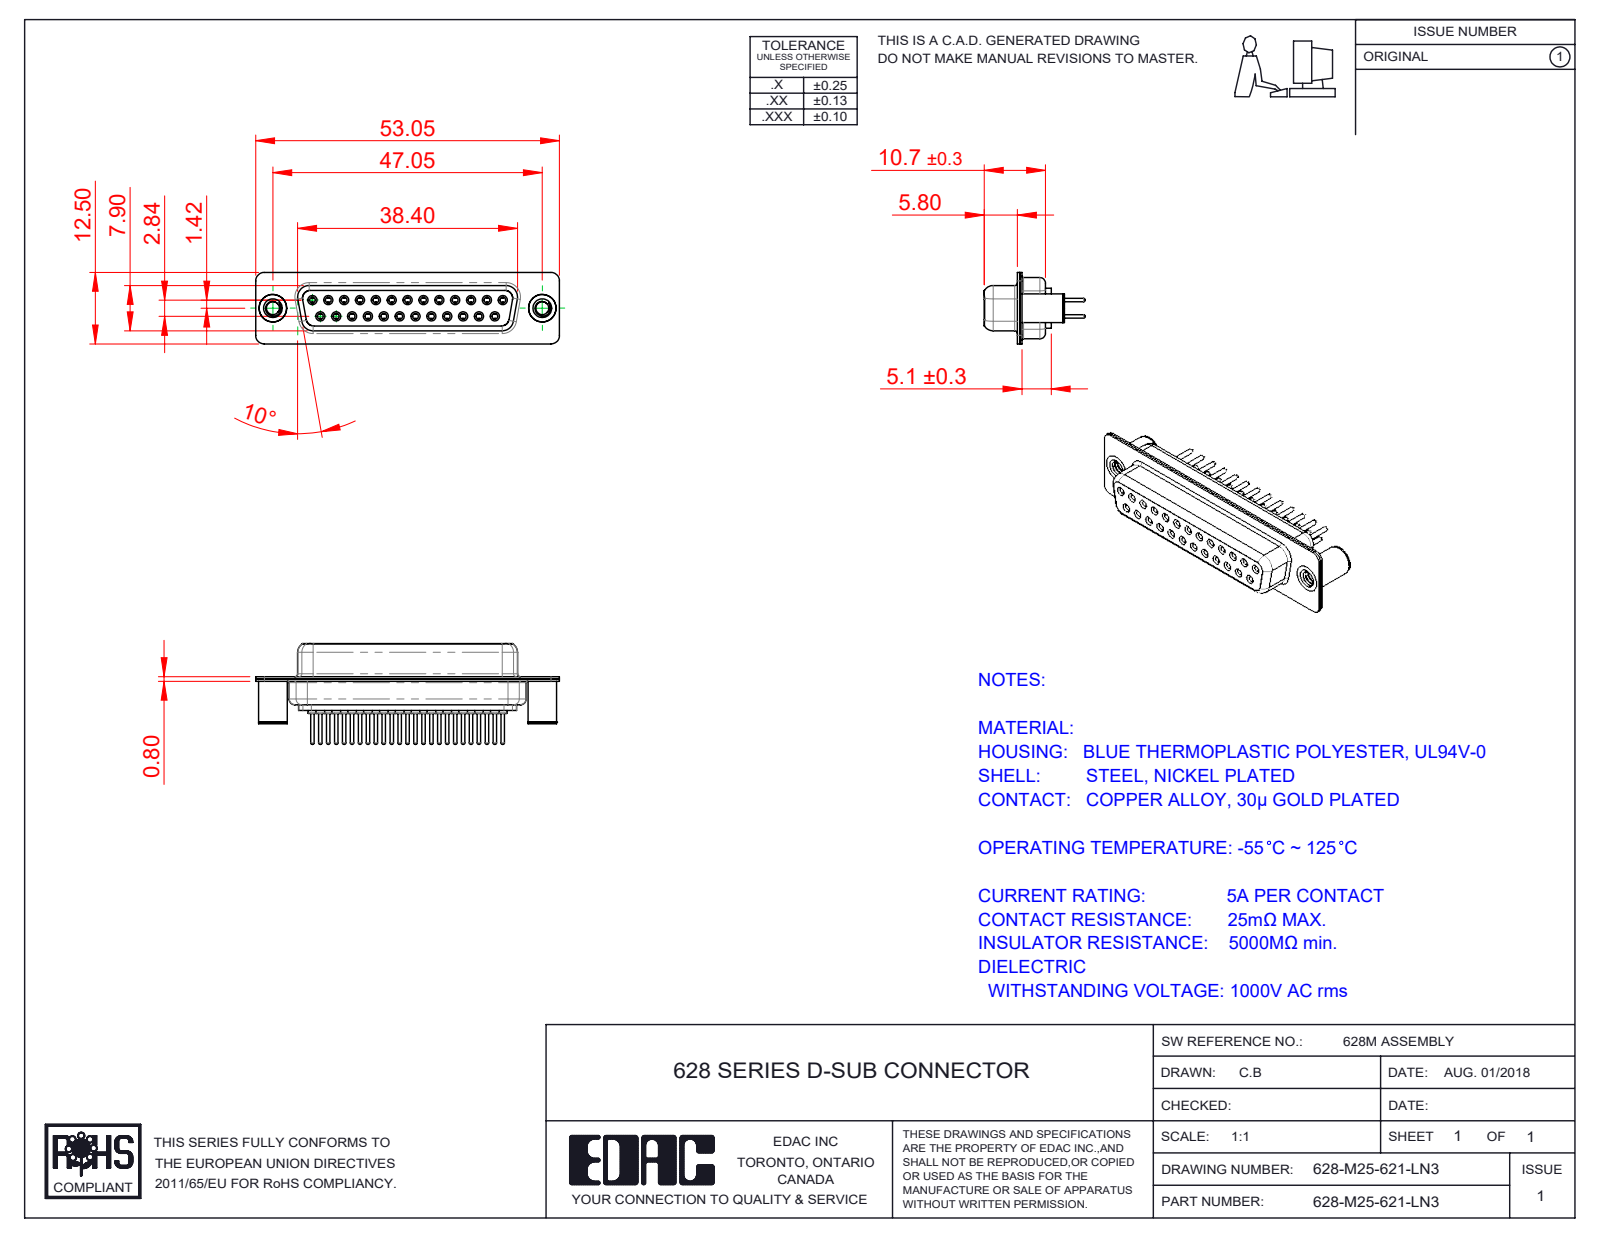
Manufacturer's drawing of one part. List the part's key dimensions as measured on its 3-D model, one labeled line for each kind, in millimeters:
Part name (STEP PRODUCT): 628M Shell Front_25 Contacts; 628M Shell Rear_25 Contacts; 628M Contact Row 2_21; 628M Housing_25 Contacts (+3 more)
STEP written by: SolidWorks 2020 (CONFIG_CONTROL_DESIGN)
Units: millimetres
Bodies: 30 solids, 1688 faces (442 planar, 636 cylindrical, 610 other)
Overall size (bounding box): 53.05 × 17.6 × 12.5
Volume: 3 863 mm³ · Surface area: 9 405 mm²
Round holes (diameter × count): ⌀1 ×25, ⌀1.1 ×25, ⌀1.7 ×25, ⌀1.8 ×25, ⌀2 ×25, ⌀2.26 ×2, ⌀3.26 ×2, ⌀4 ×2, ⌀4.8 ×2
Round bosses / shafts (diameter × count): ⌀2.2 ×25, ⌀1.6 ×25, ⌀1.5 ×25, ⌀0.6 ×25, ⌀5 ×2, ⌀4.9 ×2
Partial cylindrical surfaces — rounded edges, fillets, slot ends (radius × count): R1.5 ×16, R2 ×12, R1.35 ×8, R1.6 ×8, R0.25 ×4, R0.5 ×4, R0.6 ×4, R0.65 ×4
Main face-to-face distances: 0.4, 1.4, 0.45, 8.45, 8.9, 1.8, 6.2, 7.05, 1, 1.85
Hole centre spacings: 3.16, 2.77, 5.54, 8.31, 11.08, 13.85, 5.04, 7.49
